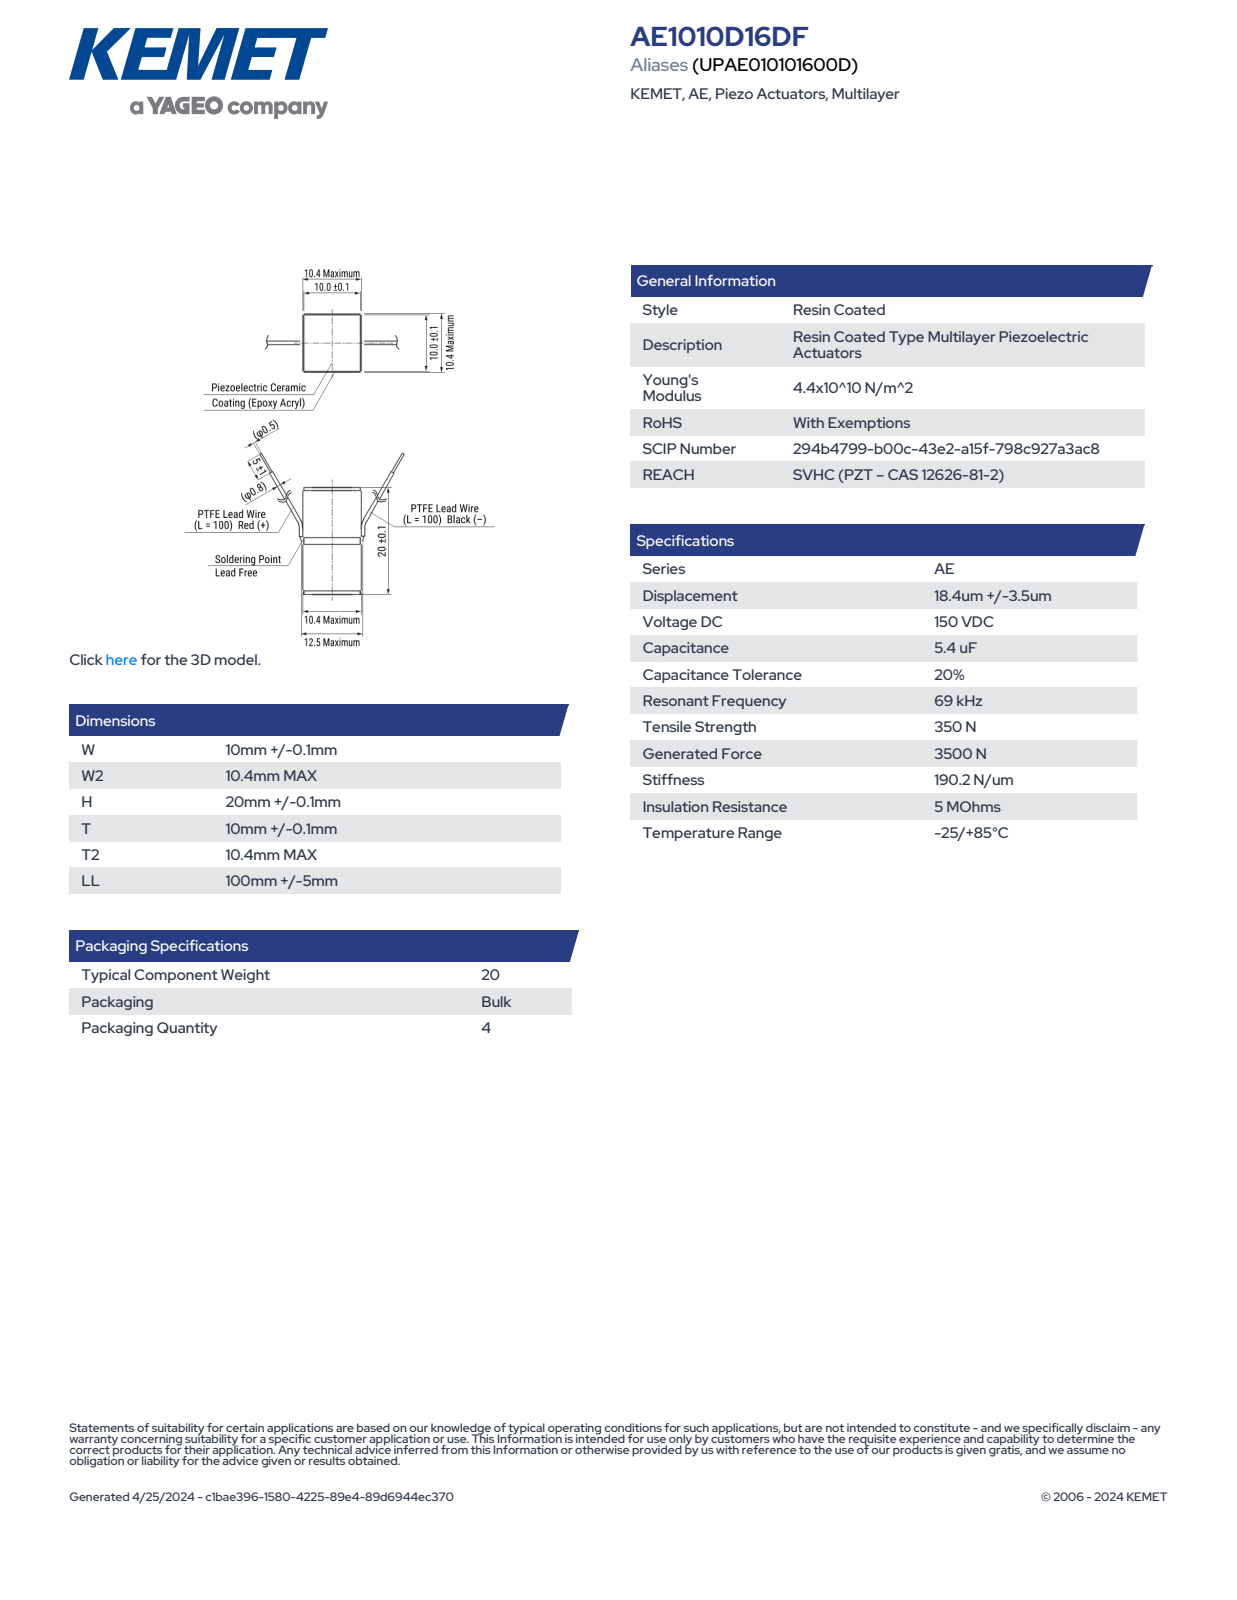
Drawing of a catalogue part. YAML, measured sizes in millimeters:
part_name: "AL_KAE1_W10.1W210.4H20.1T10.1T210.4"
step_written_by: "SolidWorks 2014 (AUTOMOTIVE_DESIGN)"
units: millimeters
bodies: {solids: 4, faces: 93, planar: 85, cylindrical: 8, other: 0}
overall_size: [20.11, 10.4, 10.4]
volume: 2051
surface_area: 1054
partial_cylinders:
  - {radius: 0.15, count: 8}
face_to_face_distances: [10.1, 10.25, 10, 9.9, 20.1, 10.4, 1.97, 18.13, 8.08, 12.02]
